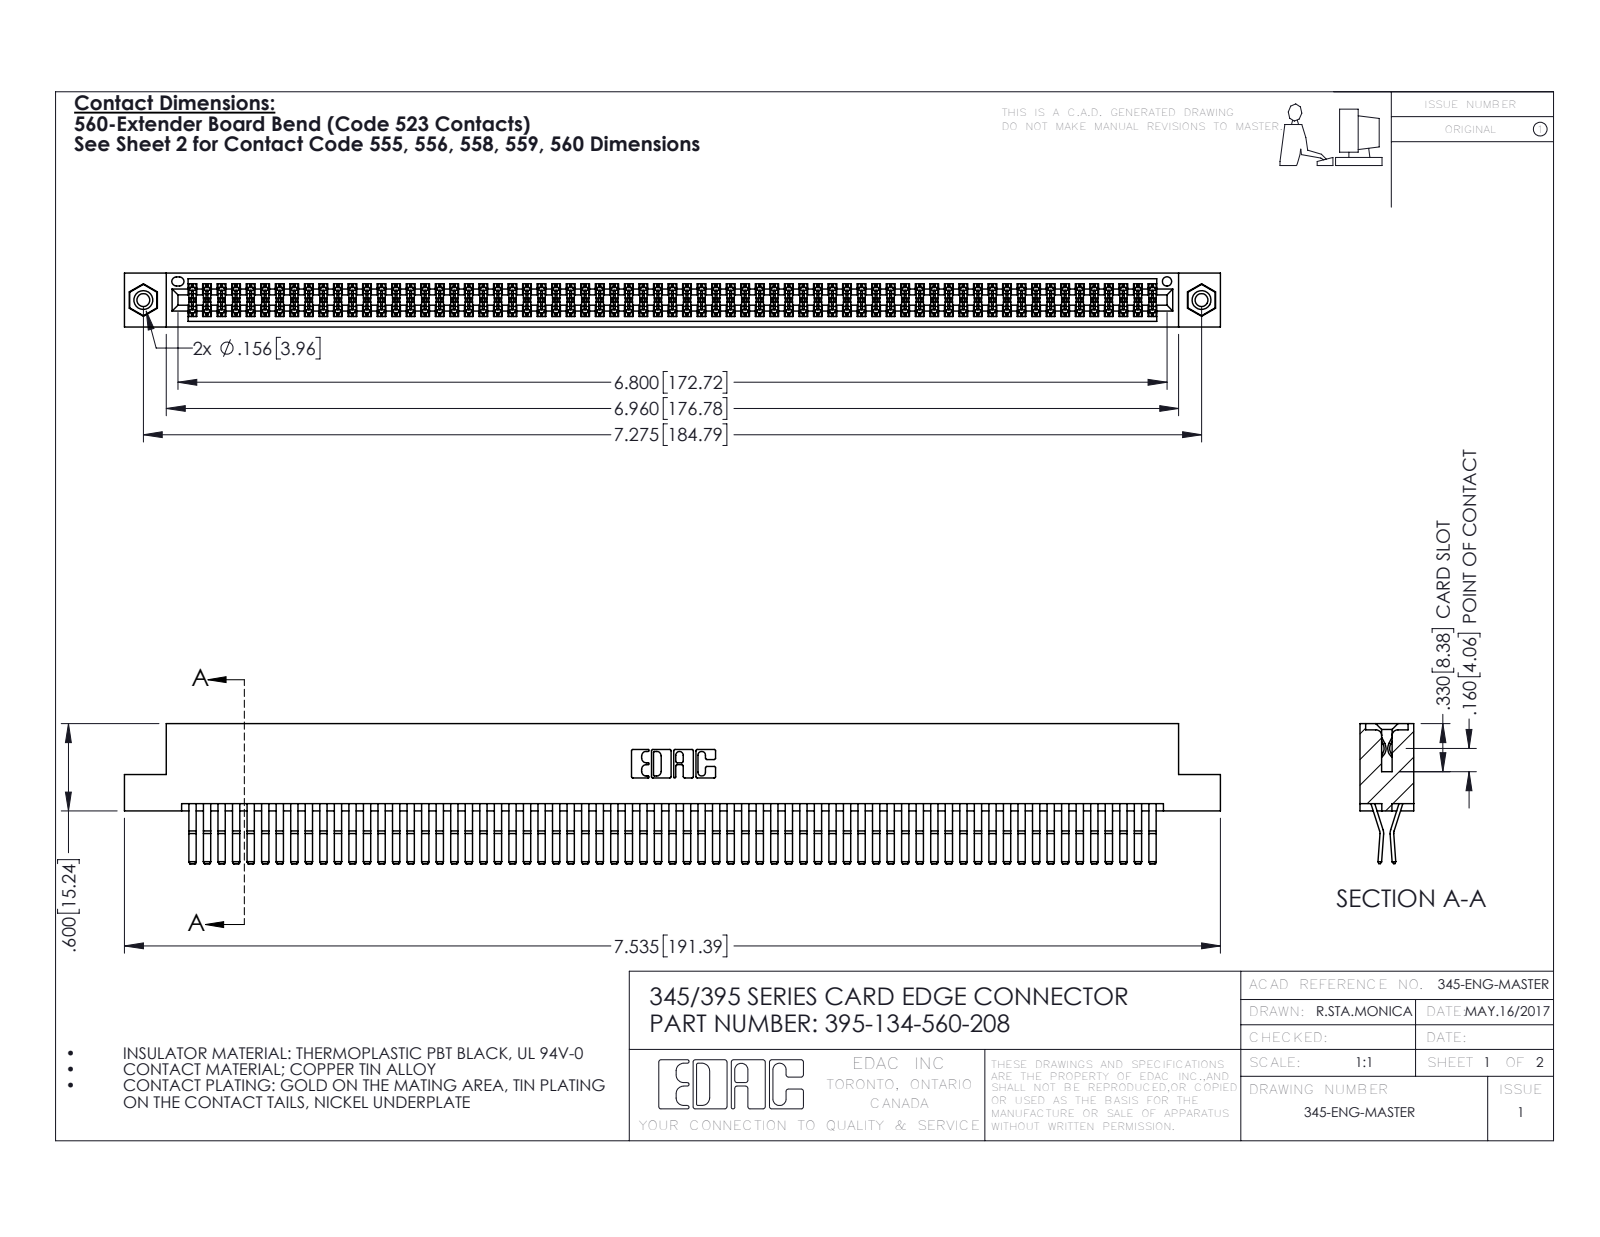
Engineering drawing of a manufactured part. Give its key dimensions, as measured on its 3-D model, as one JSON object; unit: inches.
{"part_name": "395-134-560-208; 345-292-001_560 Tail; 345 Part_Flush Mounting Lugs - 0.156 Dia-TI; 345-250-001_345-250-003-102", "step_written_by": "SolidWorks 2016 (CONFIG_CONTROL_DESIGN)", "units": "inches", "bodies": {"solids": 137, "faces": 7154, "planar": 4534, "cylindrical": 2604, "other": 16}, "overall_size": [7.535, 0.962, 0.37], "volume_in3": 1.202, "surface_area_in2": 49.4, "round_holes": [[0.089, 2], [0.125, 2], [0.156, 2], [0.064, 1]], "round_bosses_or_shafts": [[0.155, 2]], "partial_cylinders_radius": [[0.006, 201], [0.01, 22], [0.007, 6], [0.031, 6], [0.026, 3], [0.01, 2], [0.014, 2], [0.019, 2]], "face_to_face_distances": [0.025, 0.072, 0.298, 0.37, 0.2, 0.098, 0.272, 0.225, 0.175, 0.149], "hole_center_spacings": [0.27, 7.039, 7.275]}
